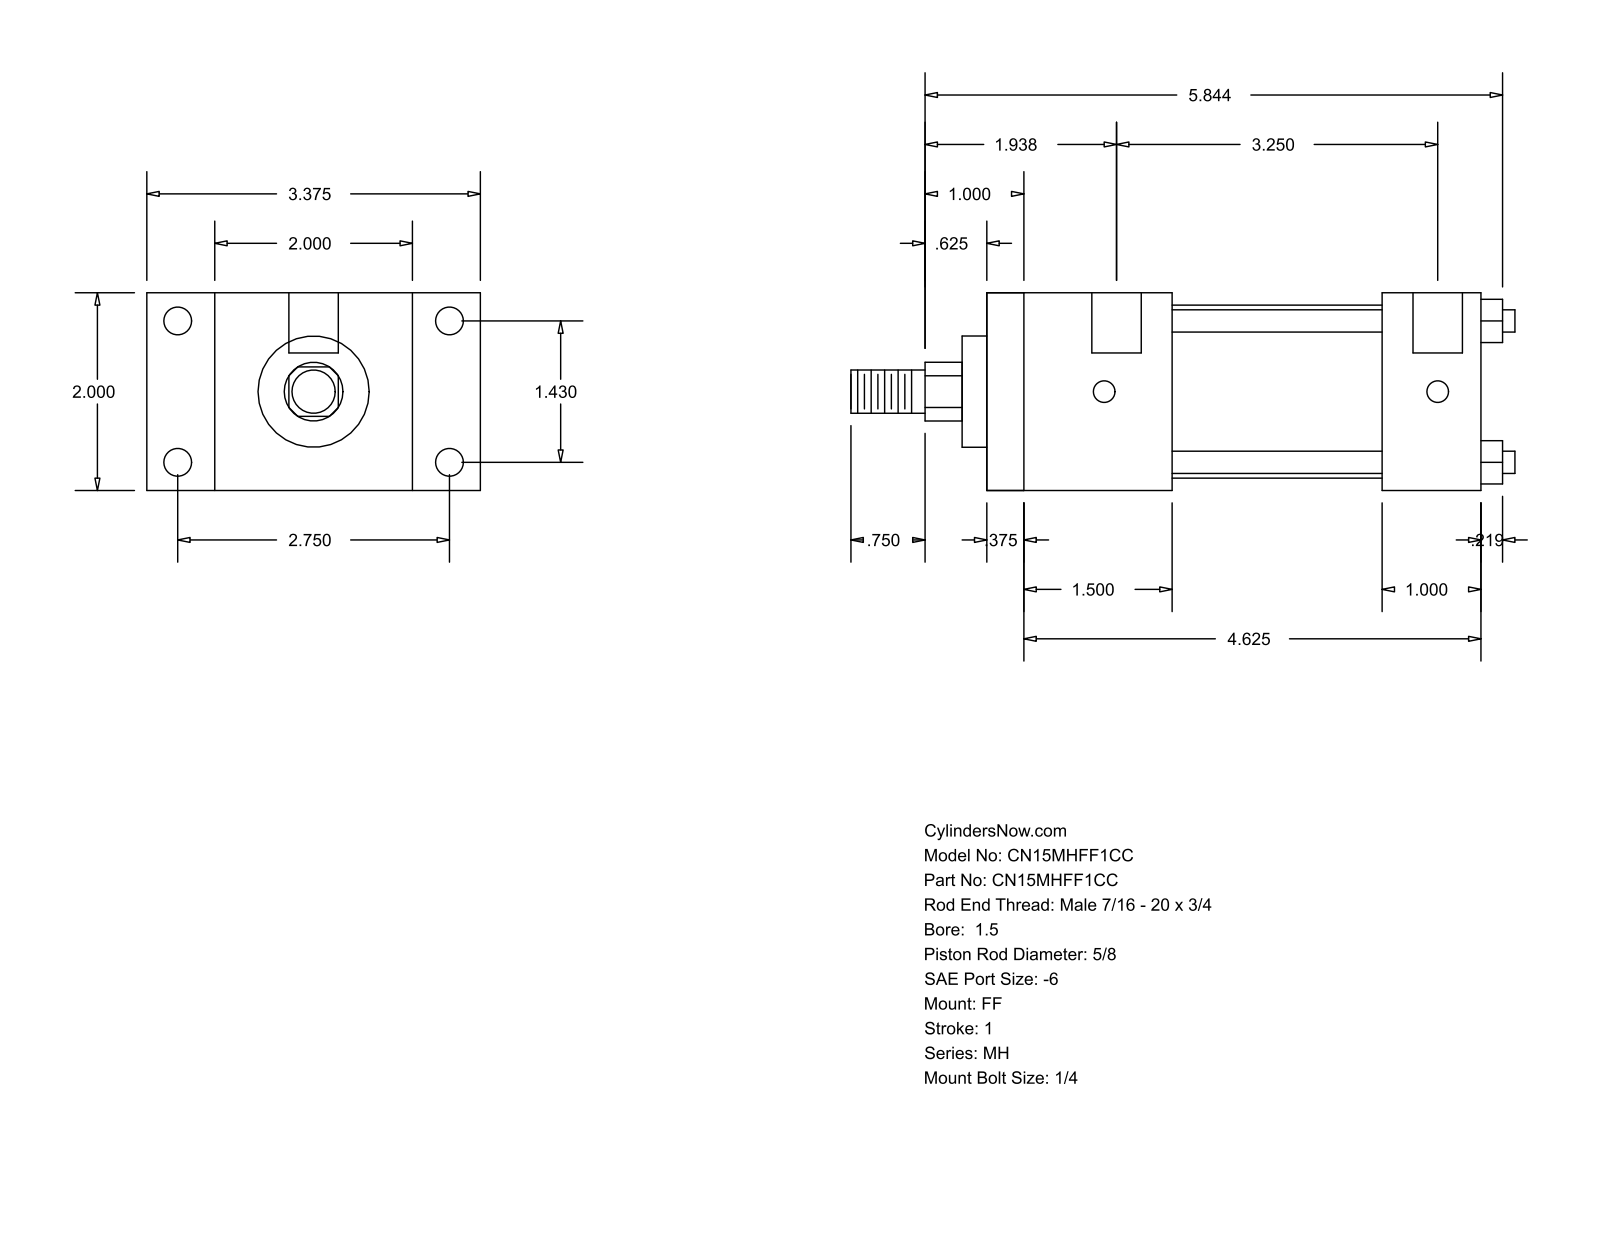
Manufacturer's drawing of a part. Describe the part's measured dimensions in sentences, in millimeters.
The part is named "MH_FF__0150_0.625". Its 3-D file was written by "GSSL Pune (CONFIG_CONTROL_DESIGN)". It is 0 solids with 92 faces: 64 planar, 28 cylindrical and 0 other. Overall it measures 170.66 by 85.72 by 50.8 millimeters. Round holes: 4 of diameter 5.56, 4 of diameter 7.14, 2 of diameter 12.7. Round bosses or shafts: 4 of diameter 5.71, 1 of diameter 44.45, 1 of diameter 28.57, 1 of diameter 15.88, 1 of diameter 11.11. Partial cylindrical surfaces (rounded edges, fillets, slot ends): 1 of radius 7.54. The main face-to-face distances are 50.8, 127, 9.52, 117.48, 53.97, 17.46, 68.26, 47.62, 38.1, 79.38. The hole center spacings are 36.32, 69.84, 78.72, 85.72, 3.17, 82.55.
